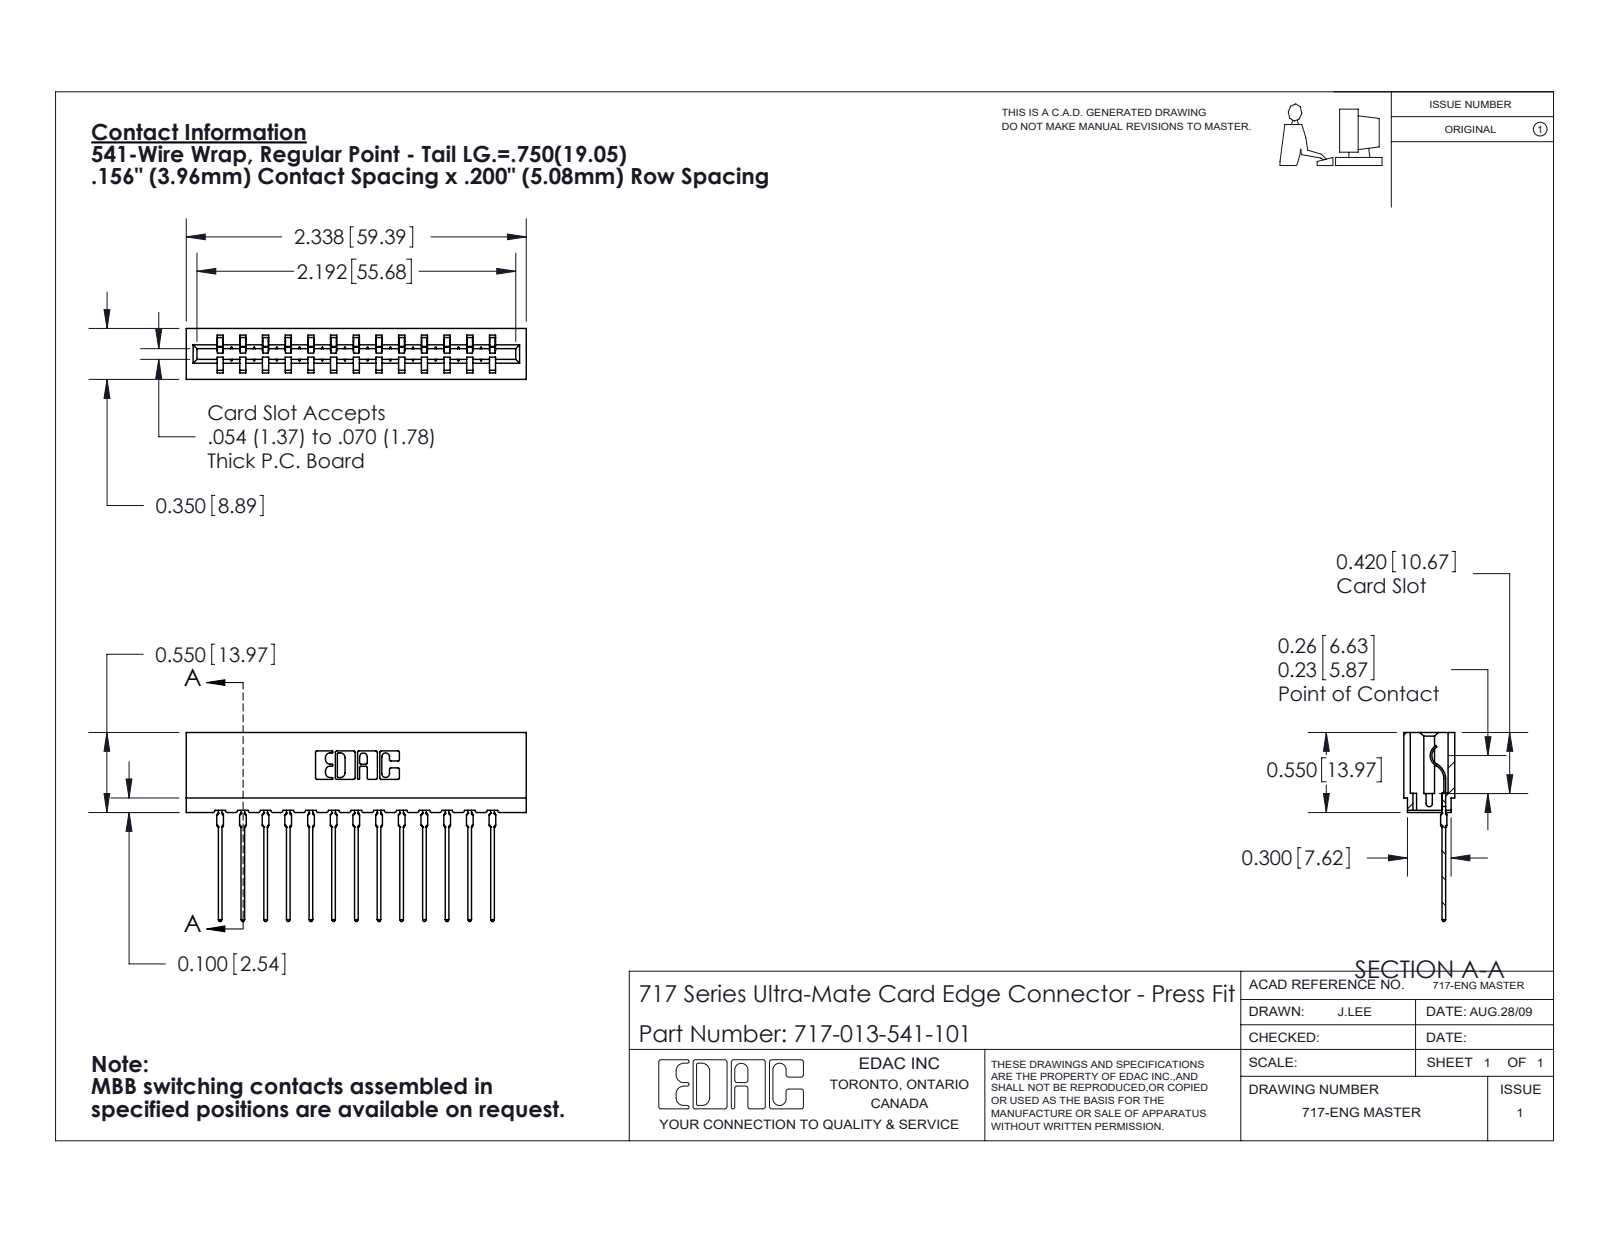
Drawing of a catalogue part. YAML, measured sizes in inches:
part_name: "717 Part_Insulator Option - 06; 745-292-001_541; 717-013-541-101"
step_written_by: "SolidWorks 2020 (CONFIG_CONTROL_DESIGN)"
units: inches
bodies: {solids: 14, faces: 1563, planar: 938, cylindrical: 287, other: 338}
overall_size: [2.338, 1.299, 0.35]
volume: 0.317
surface_area: 11.26
partial_cylinders:
  - {radius: 0.015, count: 26}
  - {radius: 0.021, count: 26}
  - {radius: 0.01, count: 22}
  - {radius: 0.007, count: 6}
  - {radius: 0.031, count: 6}
  - {radius: 0.005, count: 4}
  - {radius: 0.011, count: 4}
  - {radius: 0.026, count: 3}
face_to_face_distances: [0.212, 0.138, 0.156, 0.35, 0.624, 0.468, 0.312, 0.198, 0.074, 0.063]
